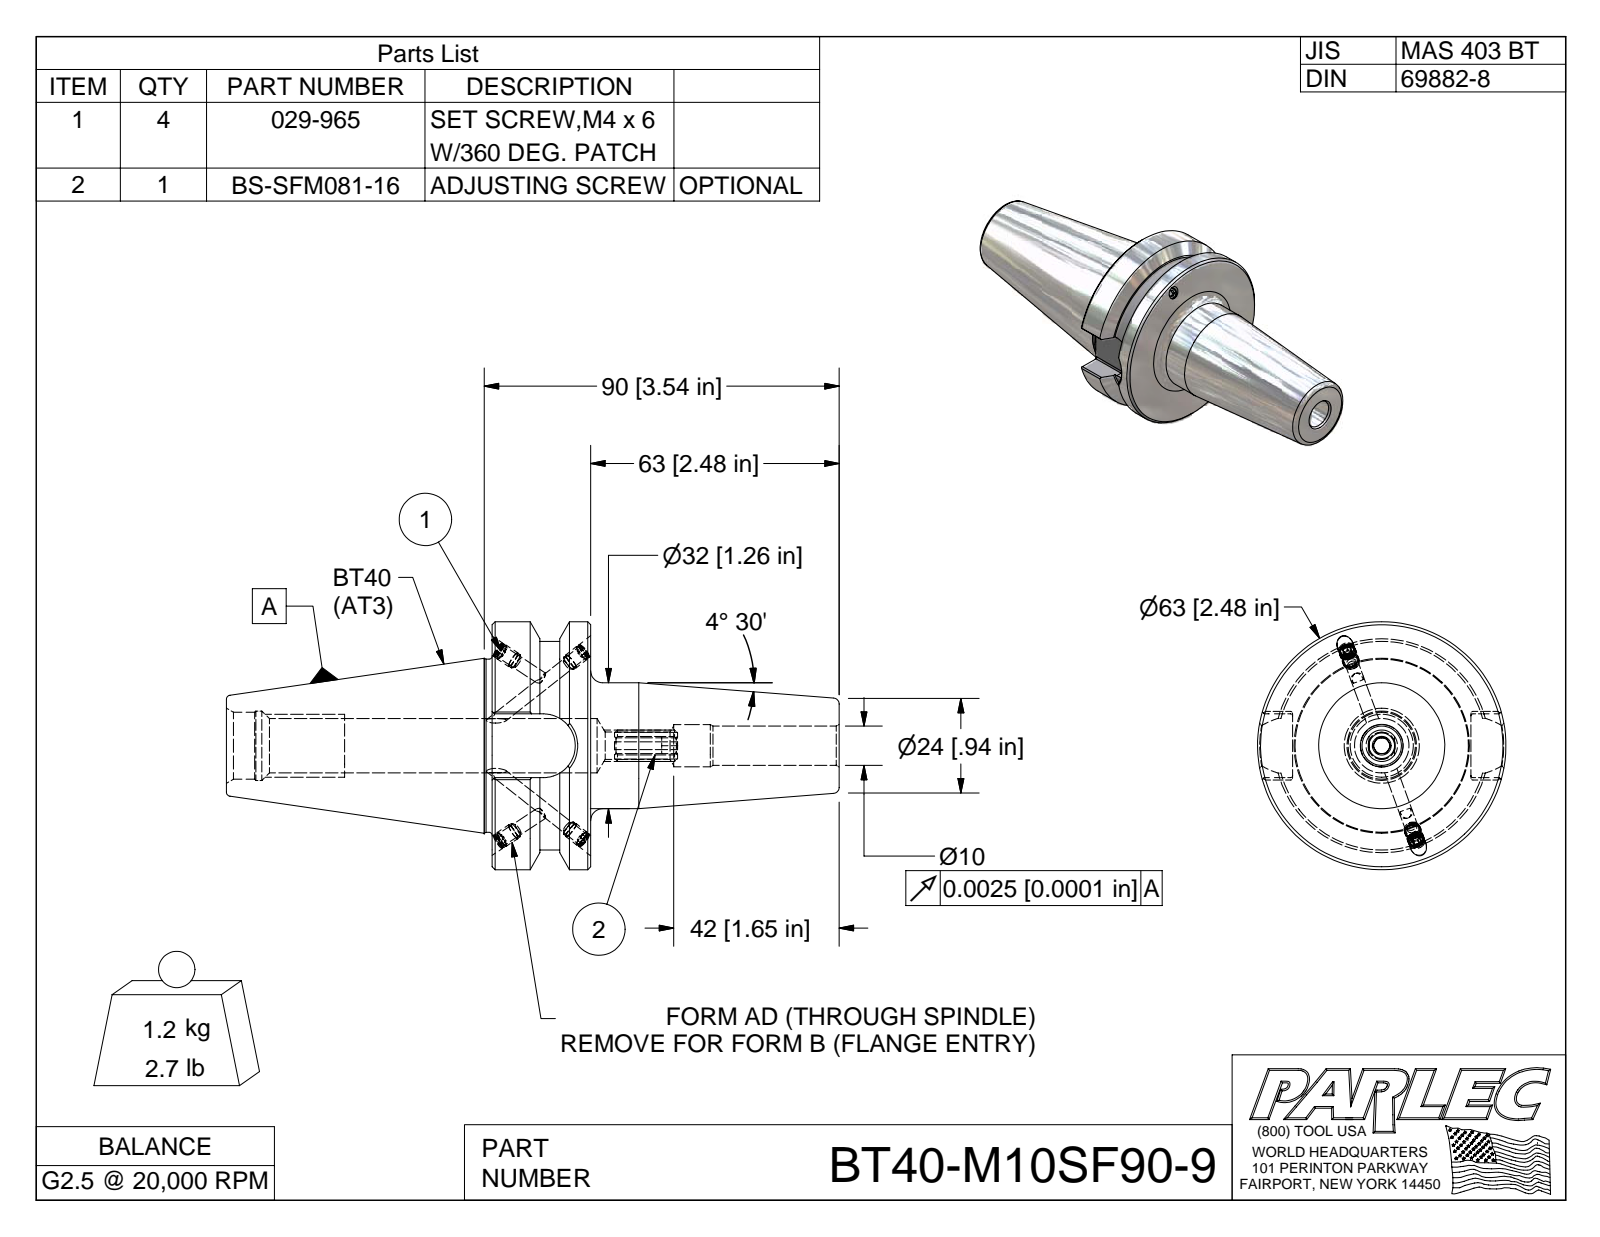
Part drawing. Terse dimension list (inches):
name: BT40-M10SF90-9; BT40BC-M10SF90-9-1; 029-965; BS-SFM081-16
written by: Autodesk Inventor 2009 (AUTOMOTIVE_DESIGN)
unit: in
bodies: 6 solids, 173 faces (79 planar, 43 cylindrical, 51 other)
size: 6.118 × 2.48 × 2.48
volume: 9.538 in³; area: 48.78 in²
holes: 4× ⌀0.13, 4× ⌀0.161, 1× ⌀0.393, 1× ⌀0.423, 1× ⌀0.694
bosses: 4× ⌀0.165, 4× ⌀0.157, 1× ⌀2.48, 1× ⌀2.087, 1× ⌀1.75, 1× ⌀1.73, 1× ⌀1.26
rounds: 8× R0.02, 1× R0.157, 1× R0.319
face distances: 0.984, 1.78, 3.465, 2.481, 2.653, 3.637, 6.119, 0.637, 0.762, 1.018
